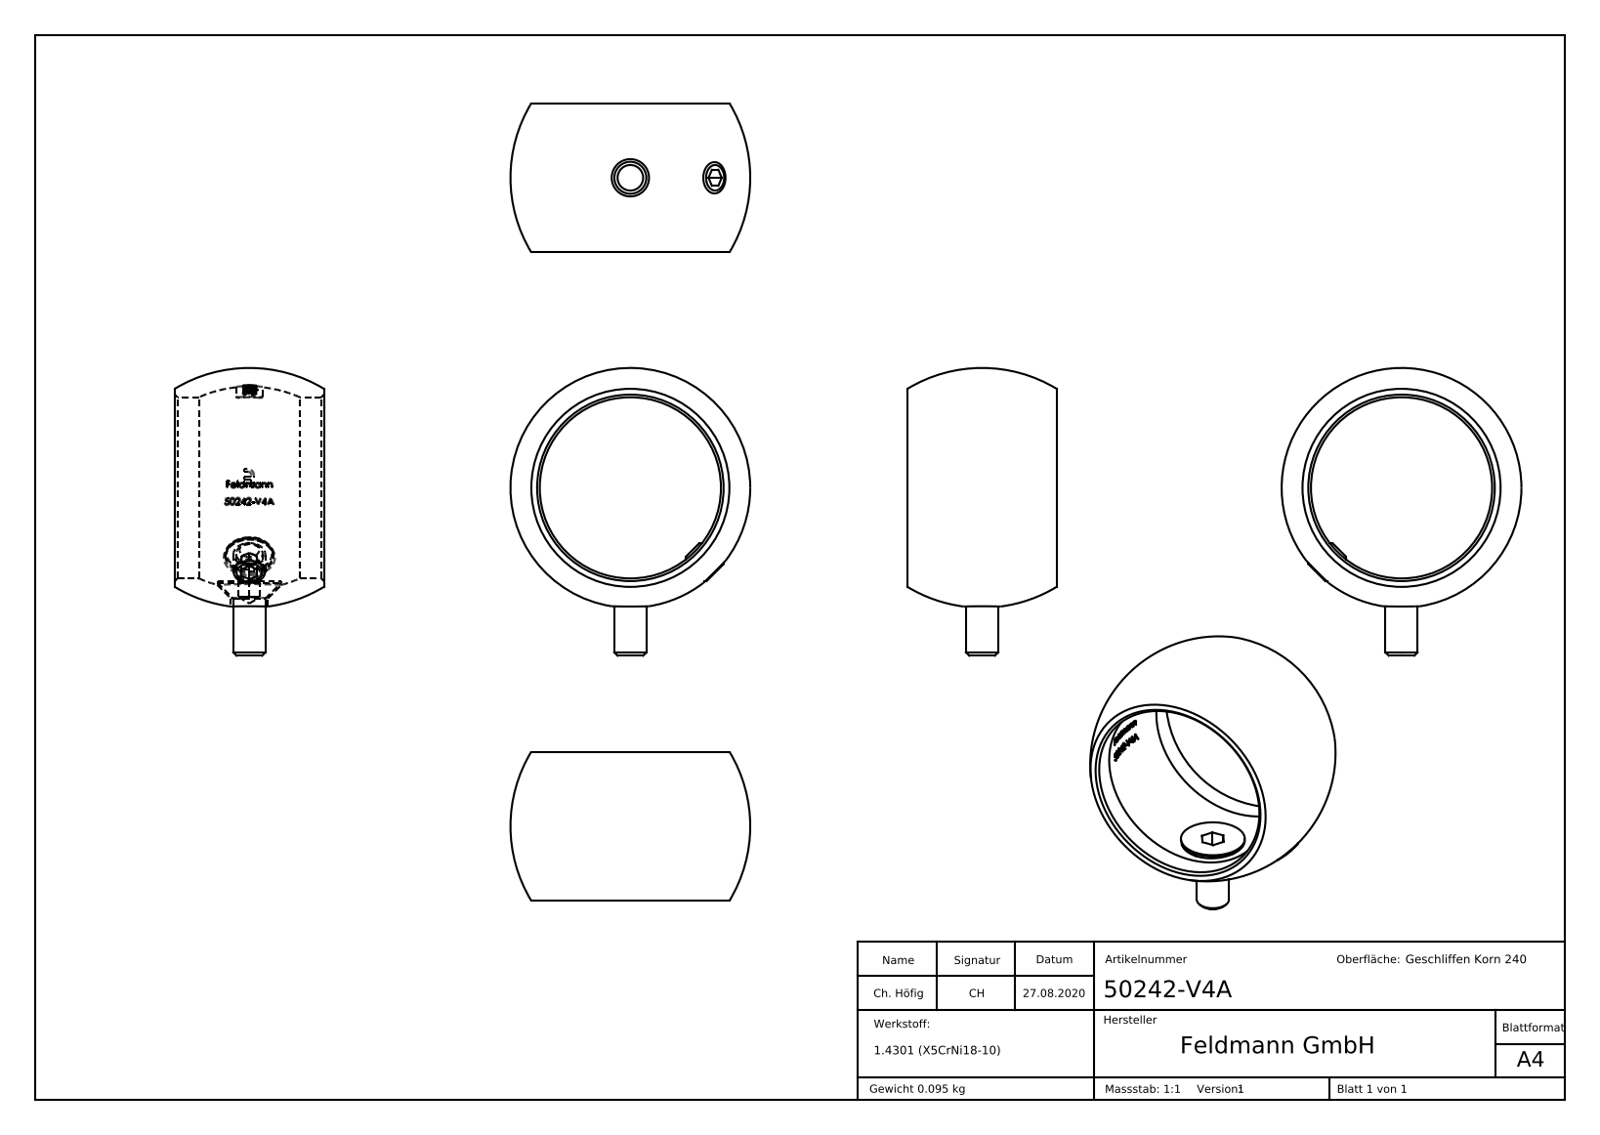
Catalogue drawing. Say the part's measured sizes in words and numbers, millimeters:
The part is named "DIN913_DIN 913 M6x6; DIN-7991 M3-M10_DIN7991 M6x14; 502XX-240 Teil1_50242-V4A Teil1; 50242-V4A". Its 3-D file was written by "SolidWorks 2018 (CONFIG_CONTROL_DESIGN)". It is 3 solids with 434 faces: 202 planar, 20 cylindrical and 212 other. Overall it measures 50.7 by 45 by 28 millimeters. Its volume is 11 864 cubic millimeters and its surface area 8 184 square millimeters. Round holes: 1 of diameter 5, 1 of diameter 7, 1 of diameter 34. Round bosses or shafts: 2 of diameter 6, 1 of diameter 12, 1 of diameter 9. Partial cylindrical surfaces (rounded edges, fillets, slot ends): 4 of radius 0.5. The main face-to-face distances are 28, 4, 3, 14, 0.5, 1, 12, 16, 3.5, 12.5.
